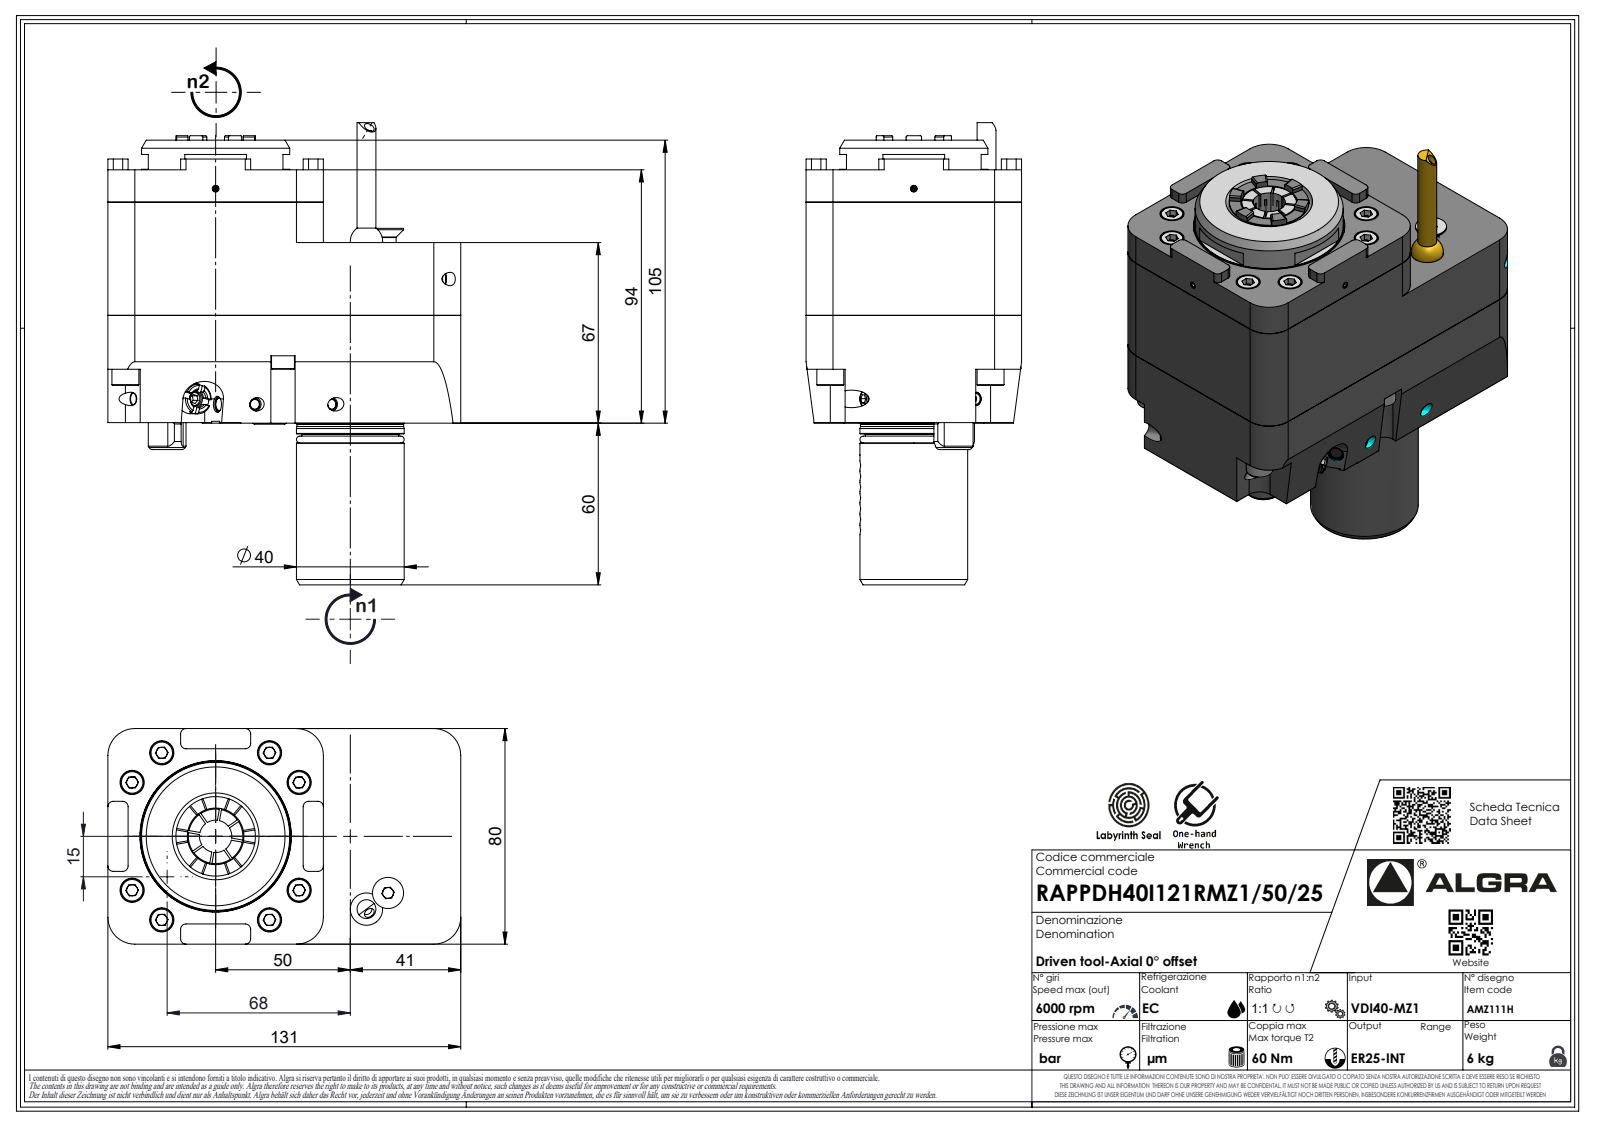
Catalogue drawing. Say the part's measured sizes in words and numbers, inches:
The part is named "RAPPDH40I121RMZ15025". Its 3-D file was written by "SolidWorks 2023 (AUTOMOTIVE_DESIGN)". It is 1 solid with 558 faces: 371 planar, 96 cylindrical and 91 other. Overall it measures 6.752 by 5.157 by 3.15 inches. Its volume is 58.02 cubic inches and its surface area 107.1 square inches. Round holes: 1 of diameter 0.083, 1 of diameter 0.157. Round bosses or shafts: 1 of diameter 2.165, 1 of diameter 1.575, 1 of diameter 1.559, 1 of diameter 1.417, 1 of diameter 0.433, 1 of diameter 0.276, 1 of diameter 0.251, 1 of diameter 0.067. Partial cylindrical surfaces (rounded edges, fillets, slot ends): 17 of radius 0.079, 7 of radius 0.012, 7 of radius 0.013, 7 of radius 0.02, 7 of radius 0.146, 6 of radius 0.394, 4 of radius 0.197, 2 of radius 0.059. The main face-to-face distances are 3.15, 5.157, 2.638, 1.063, 3.701, 2.63, 3.693, 1.496, 4.134, 4.126.
